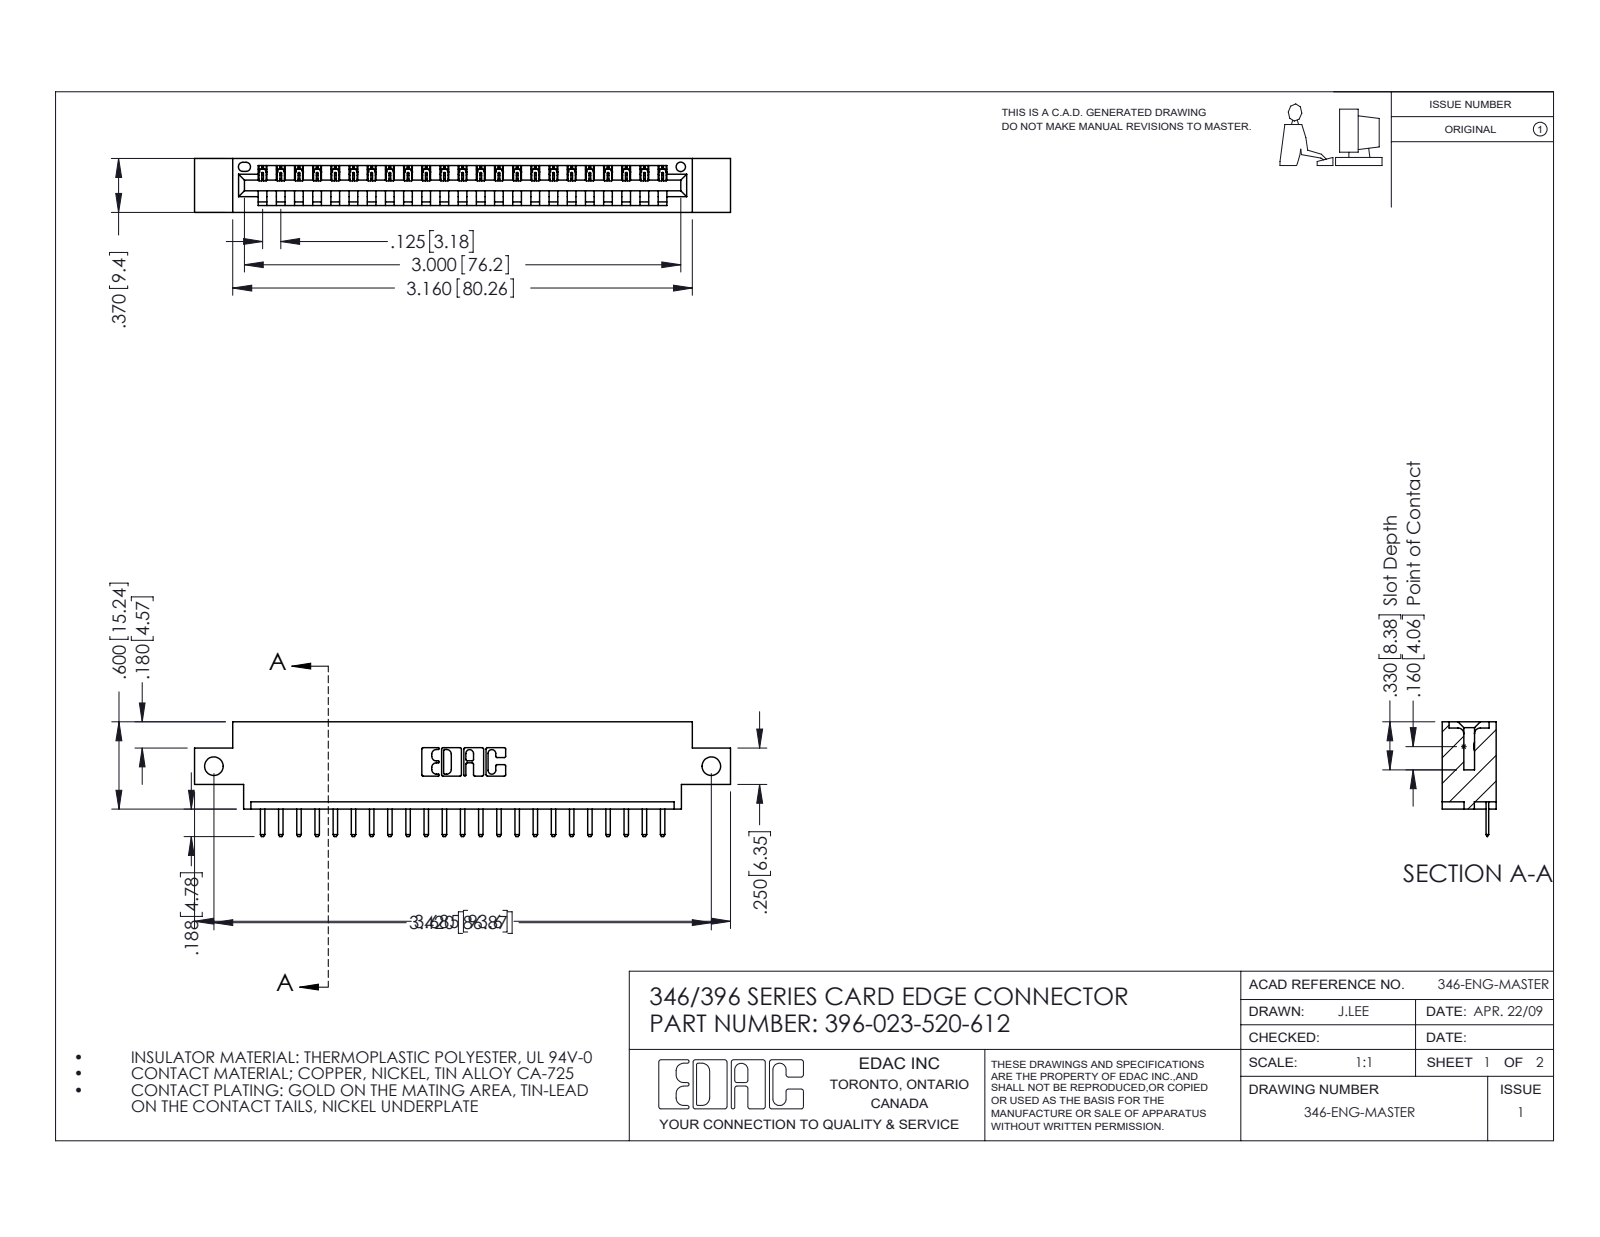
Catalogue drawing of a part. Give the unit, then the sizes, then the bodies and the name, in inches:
Units: inches
Overall size (bounding box): 3.685 × 0.788 × 0.37
Round holes (diameter × count): ⌀0.128 ×2, ⌀0.064 ×1
Partial cylindrical surfaces — rounded edges, fillets, slot ends (radius × count): R0.01 ×48, R0.006 ×46, R0.01 ×22, R0.007 ×6, R0.031 ×6, R0.026 ×3, R0.031 ×2, R0.04 ×2
Main face-to-face distances: 0.37, 0.048, 0.322, 0.25, 0.148, 0.222, 0.1, 0.174, 0.072, 0.298
Hole centre spacings: 3.42
Volume: 0.52 in³ · Surface area: 15.87 in²
Bodies: 24 solids, 1552 faces (1046 planar, 506 cylindrical, 0 other)
Part name (STEP PRODUCT): 396-023-520-612; 346 Part_0.170 Offset - Side Mount; 345-292-001_345-293-120
STEP written by: SolidWorks 2016 (CONFIG_CONTROL_DESIGN)
